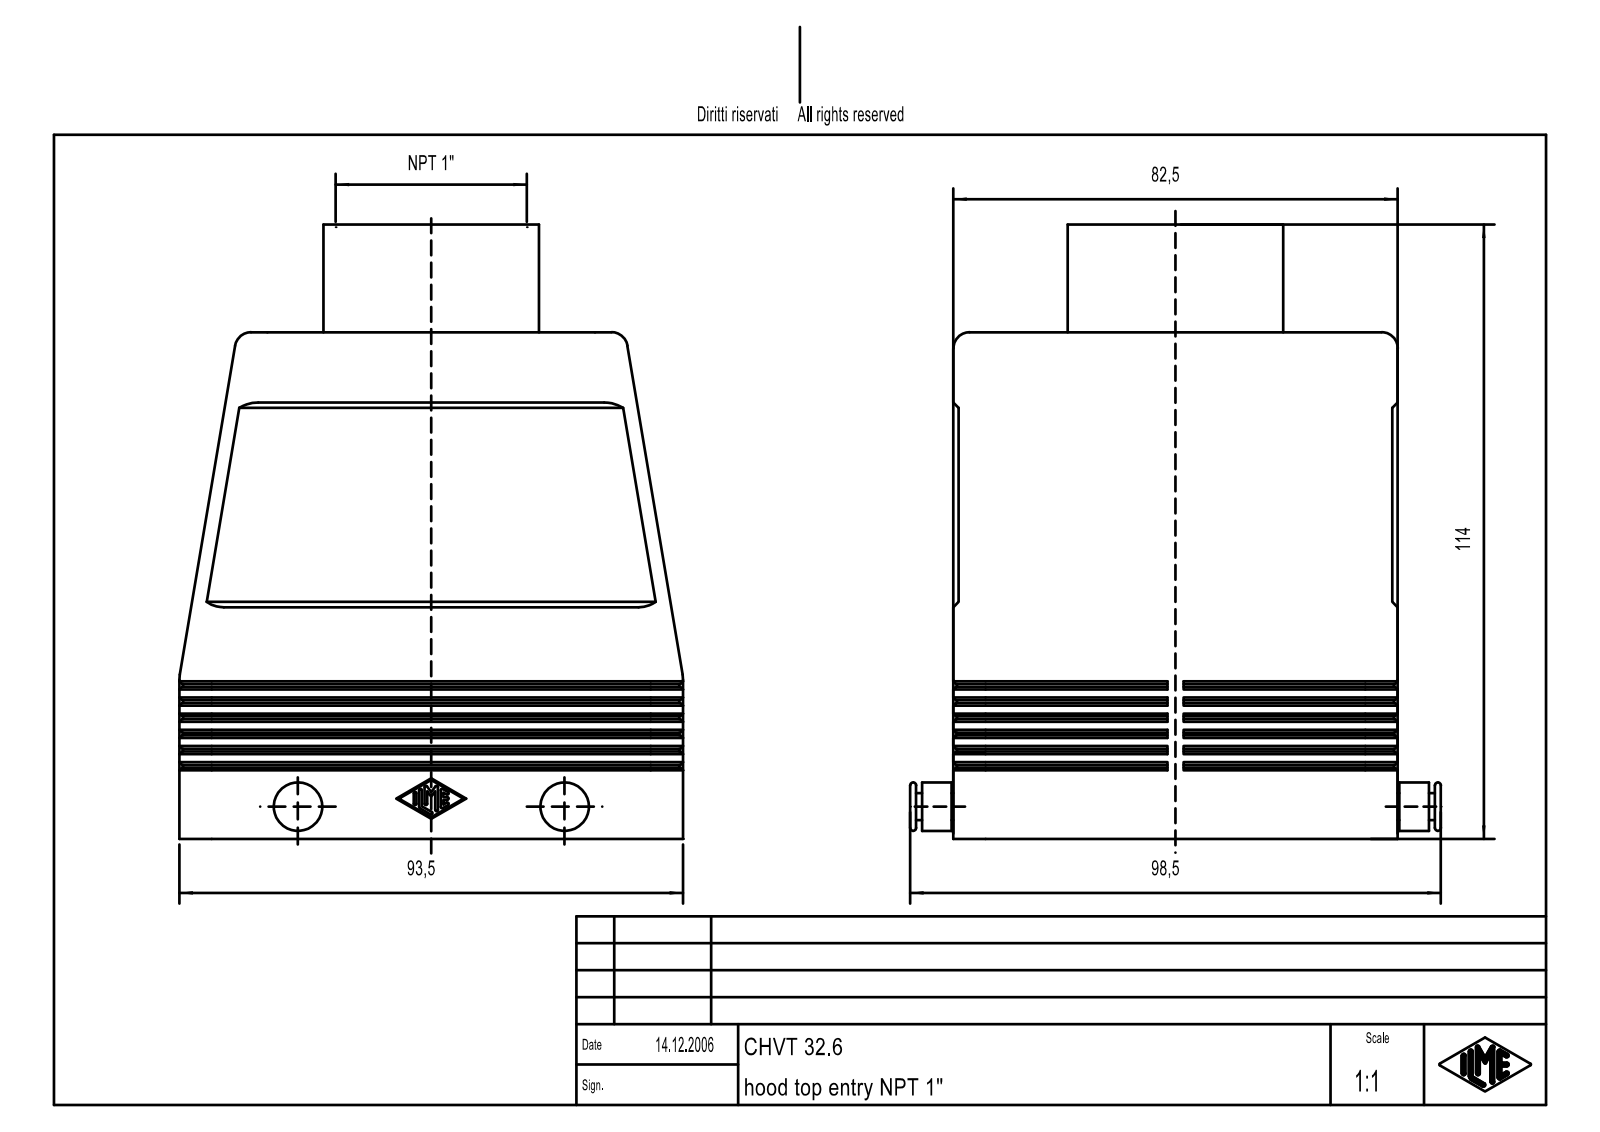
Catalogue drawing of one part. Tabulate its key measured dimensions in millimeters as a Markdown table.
| quantity | value |
| --- | --- |
| part name | MSBO10545 |
| STEP written by | Creo Elements/Direct Modeling 18.0B 02-Dec-2011 (C) Parametric Technology GmbH (AUTOMOTIVE_DESIGN) |
| units | millimeters |
| bodies | 1 solid, 529 faces (277 planar, 154 cylindrical, 98 other) |
| overall size | 114 × 98.5 × 93.5 |
| volume | 166 710 mm³ |
| surface area | 80 642 mm² |
| round holes (diameter × count) | 3.5 × 8, 2.46 × 6, 2.46 × 2, 51 × 1 |
| round bosses / shafts (diameter × count) | 9 × 2, 5 × 2, 65 × 1, 49 × 1, 48 × 1, 40 × 1 |
| partial cylindrical surfaces (radius × count) | 0.25 × 14, 2 × 12, 6 × 10, 3 × 4, 5.3 × 4 |
| main face-to-face distances | 4, 78.5, 3, 1, 74.5, 82.5, 81.5, 77.5, 7, 71.5 |
| hole center spacings | 27, 35, 38.96, 49.62, 77.5, 82.07, 85.04, 8 |
